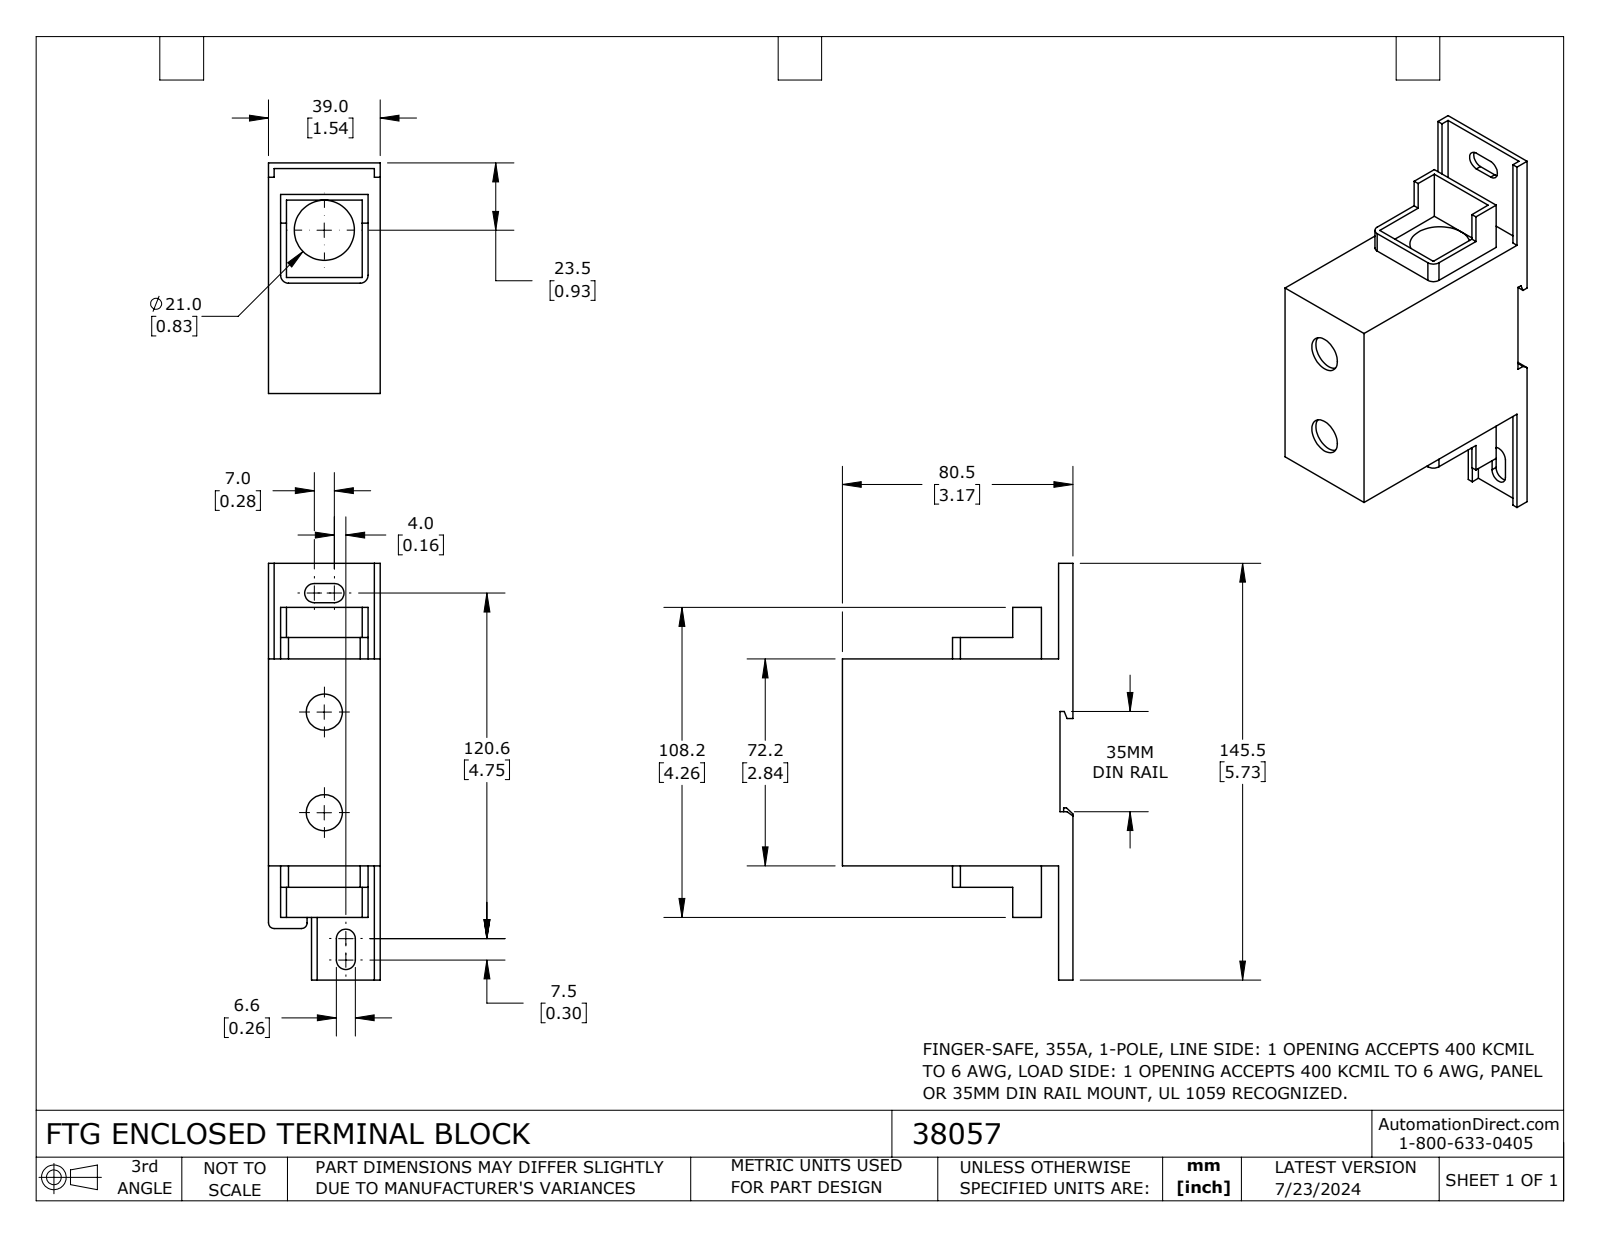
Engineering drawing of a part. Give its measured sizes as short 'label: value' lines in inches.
name: 38057
written by: SolidWorks 2023 (CONFIG_CONTROL_DESIGN)
unit: in
bodies: 1 solid, 95 faces (78 planar, 17 cylindrical, 0 other)
size: 5.728 × 3.169 × 1.535
volume: 12.57 in³; area: 62.4 in²
holes: 2× ⌀0.496, 1× ⌀0.827
rounds: 2× R0.079, 2× R0.108, 2× R0.13, 2× R0.132
face distances: 1.535, 0.079, 3.169, 2.843, 3.091, 0.098, 0.433, 2.992, 0.167, 0.177
hole spacings: 1.382
